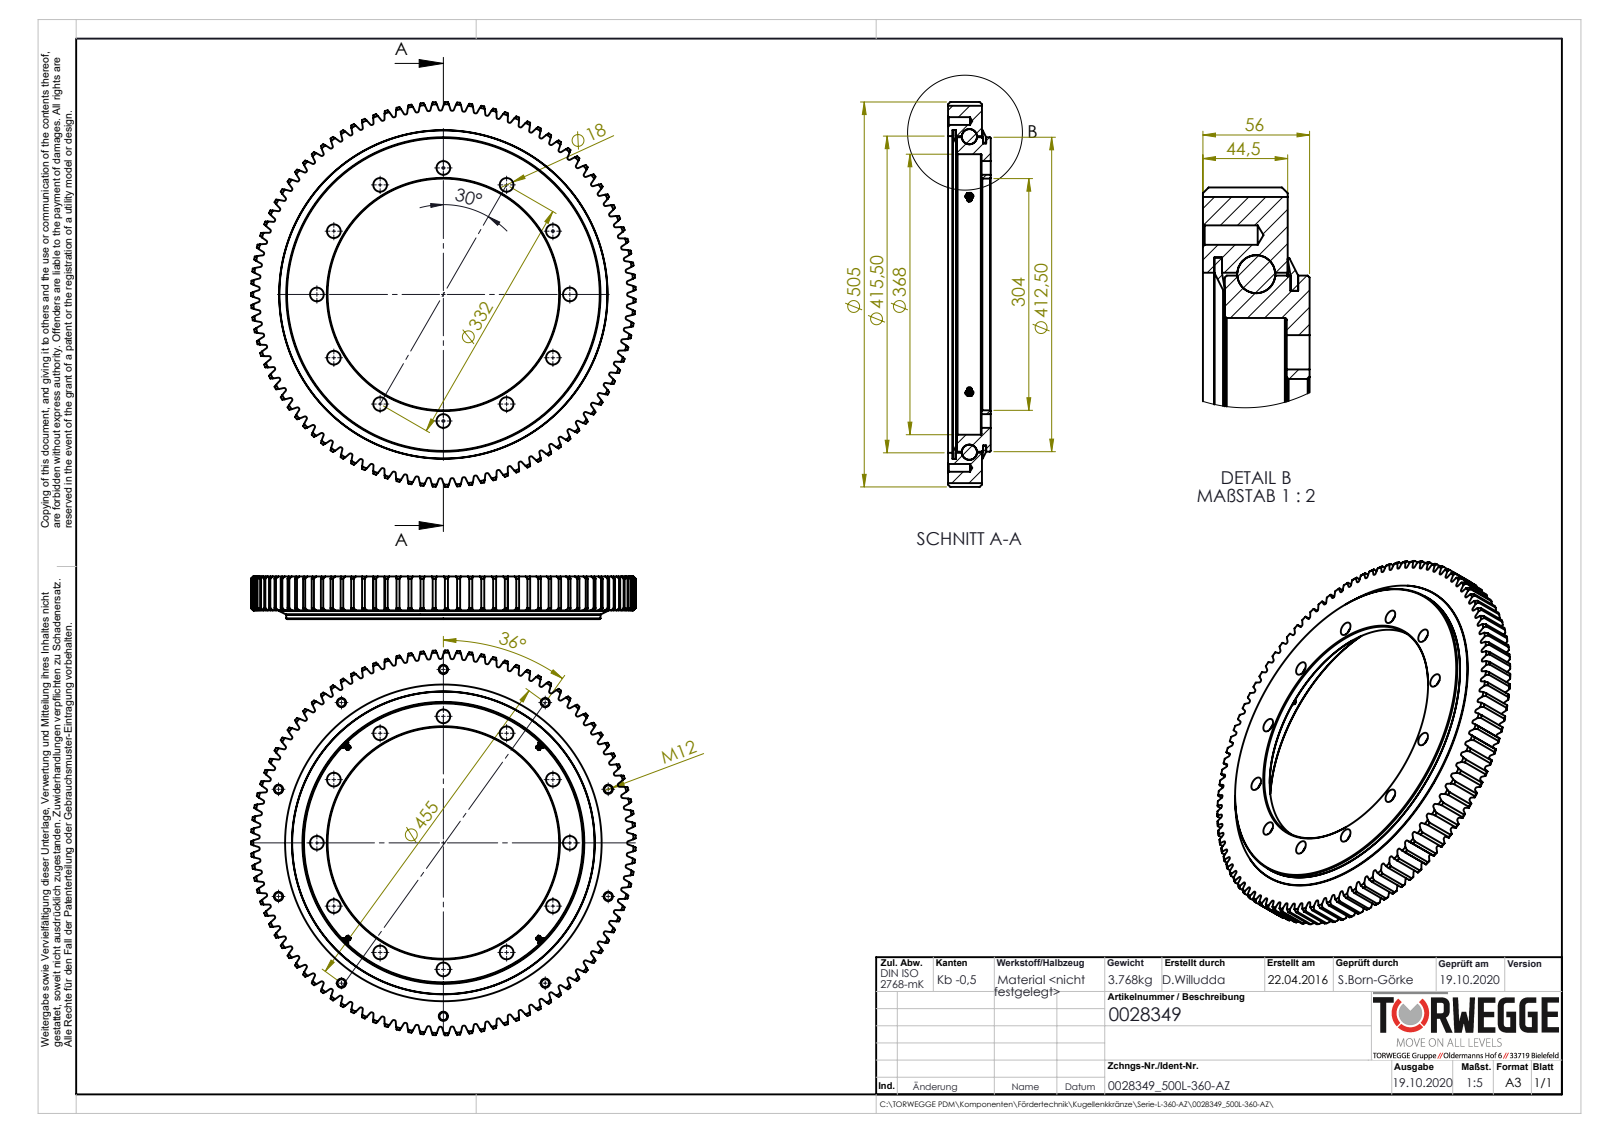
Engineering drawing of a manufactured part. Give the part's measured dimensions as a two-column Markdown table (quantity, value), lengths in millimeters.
| quantity | value |
| --- | --- |
| part name | 0028349 |
| STEP written by | SolidWorks 2018 (AUTOMOTIVE_DESIGN) |
| units | millimeters |
| bodies | 13 solids, 796 faces (61 planar, 224 cylindrical, 511 other) |
| overall size | 504.98 × 504.93 × 56 |
| volume | 3 516 000 mm³ |
| surface area | 726 990 mm² |
| round holes (diameter × count) | 18 × 12, 10.2 × 10, 1.5 × 4, 2 × 4, 4.5 × 3, 7 × 2, 5 × 1, 22 × 1, 304 × 1, 368 × 1, 396.5 × 1, 415.5 × 1 |
| round bosses / shafts (diameter × count) | 8 × 4, 4 × 4, 412.5 × 1, 21.9 × 1 |
| partial cylindrical surfaces (radius × count) | 252.5 × 1 |
| main face-to-face distances | 11.5, 44.5, 6, 56, 44, 5.5, 10, 46, 1.5, 34.5 |
| hole center spacings | 166, 85.93, 234.76, 287.52, 320.69, 227.5, 432.73, 140.6 |
